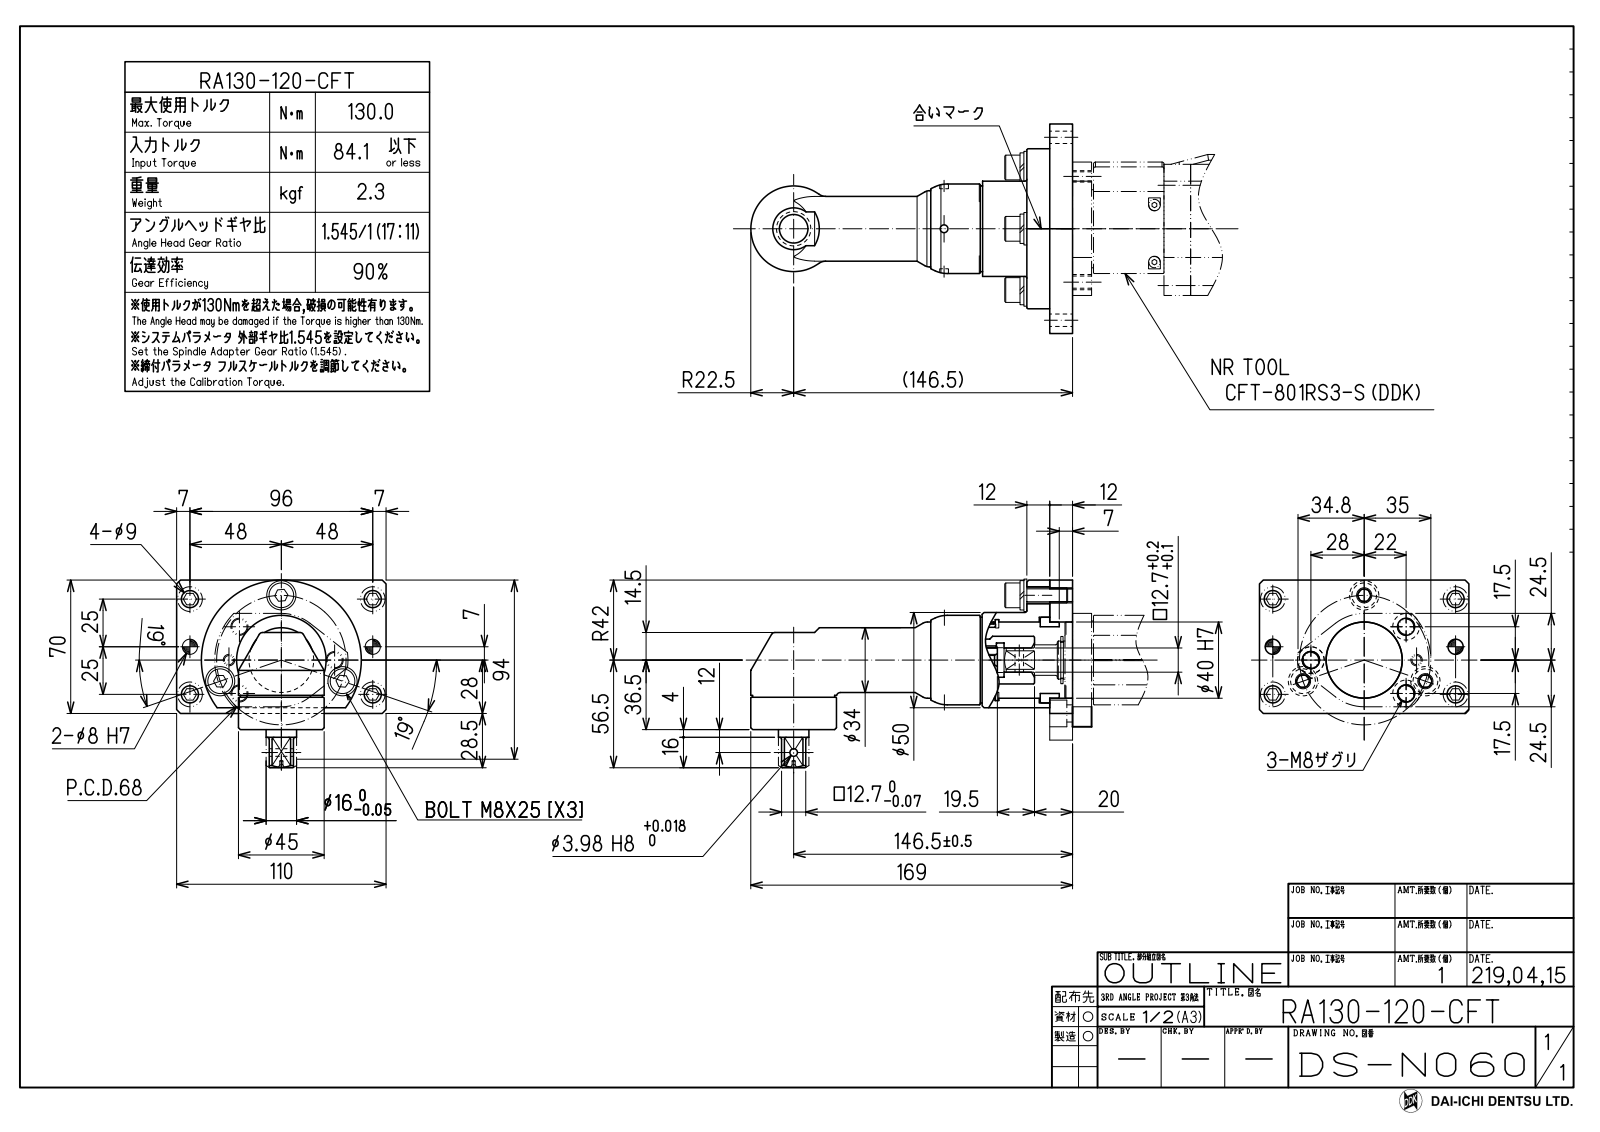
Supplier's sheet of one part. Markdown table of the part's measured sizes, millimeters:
| quantity | value |
| --- | --- |
| part name | RA130-120-CFT(DS-N060) |
| STEP written by | Autodesk Inventor 2019 (AUTOMOTIVE_DESIGN) |
| units | millimeters |
| bodies | 1 solid, 254 faces (123 planar, 84 cylindrical, 47 other) |
| overall size | 169 × 110 × 99 |
| volume | 317 630 mm³ |
| surface area | 62 588 mm² |
| round holes (diameter × count) | 9 × 7, 4.1 × 4, 4.92 × 3, 8.2 × 3, 8.4 × 3, 14 × 3, 4.6 × 2, 8 × 2, 1.6 × 1, 3.98 × 1, 15 × 1, 18 × 1 |
| round bosses / shafts (diameter × count) | 17 × 3, 15.4 × 3, 13 × 3, 8 × 3, 45 × 2, 50 × 1, 47 × 1, 43 × 1 |
| partial cylindrical surfaces (radius × count) | 1 × 8, 4.2 × 6, 29.8 × 1, 38.2 × 1, 42 × 1 |
| main face-to-face distances | 12, 24, 70, 8.5, 3, 78.5, 17, 7, 11.5, 67 |
| hole center spacings | 24.04, 34, 17, 25, 96, 99.2, 17.3, 28.11 |
